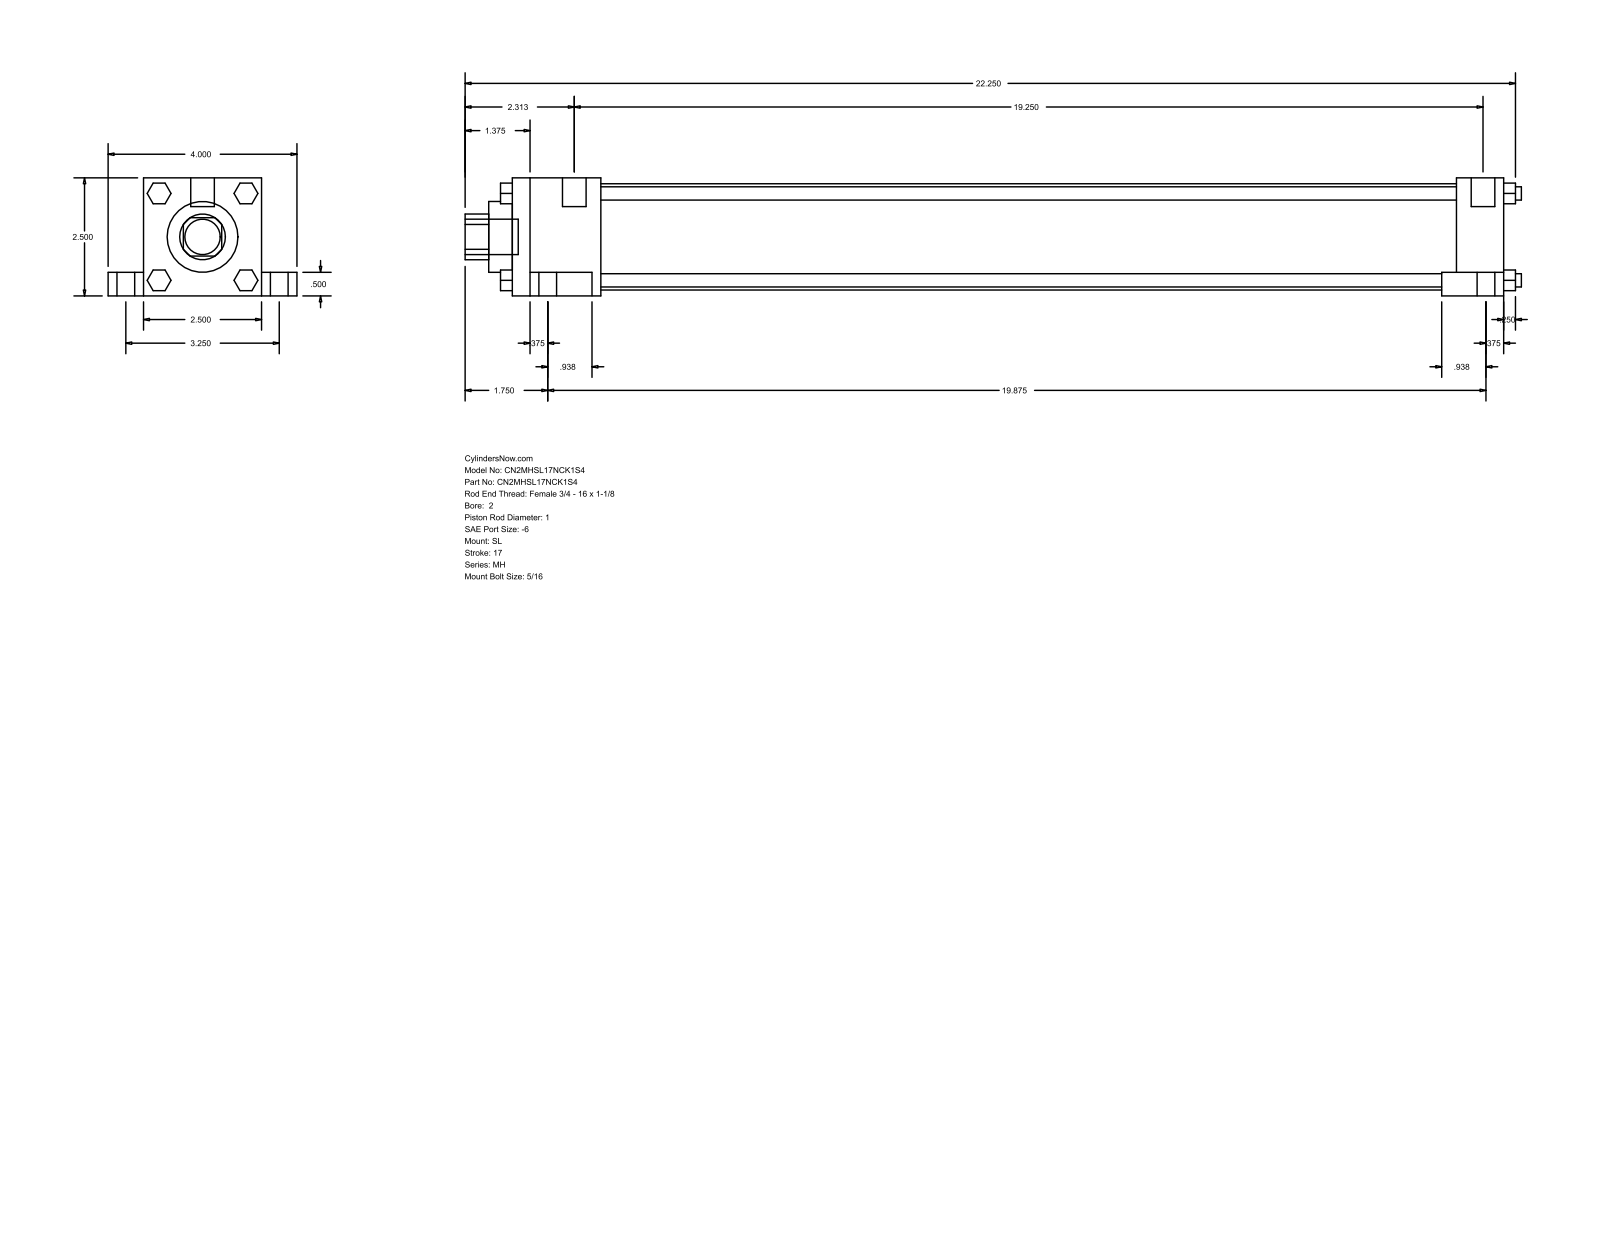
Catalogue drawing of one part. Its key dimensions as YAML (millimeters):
part_name: "MH_SL__0200_1"
step_written_by: "GSSL Pune (CONFIG_CONTROL_DESIGN)"
units: millimeters
bodies: {solids: 0, faces: 148, planar: 112, cylindrical: 36, other: 0}
overall_size: [568.33, 101.6, 63.5]
round_holes:
  - {diameter: 25.4, count: 1}
  - {diameter: 38.1, count: 1}
  - {diameter: 57.15, count: 1}
round_bosses_or_shafts:
  - {diameter: 15.88, count: 4}
  - {diameter: 9.53, count: 4}
  - {diameter: 7.14, count: 4}
  - {diameter: 5.56, count: 4}
  - {diameter: 12.7, count: 2}
  - {diameter: 19.05, count: 1}
partial_cylinders:
  - {radius: 12.29, count: 1}
face_to_face_distances: [63.5, 533.4, 12.7, 19.05, 50.8, 82.55, 25.4, 9.52, 508, 47.63]
